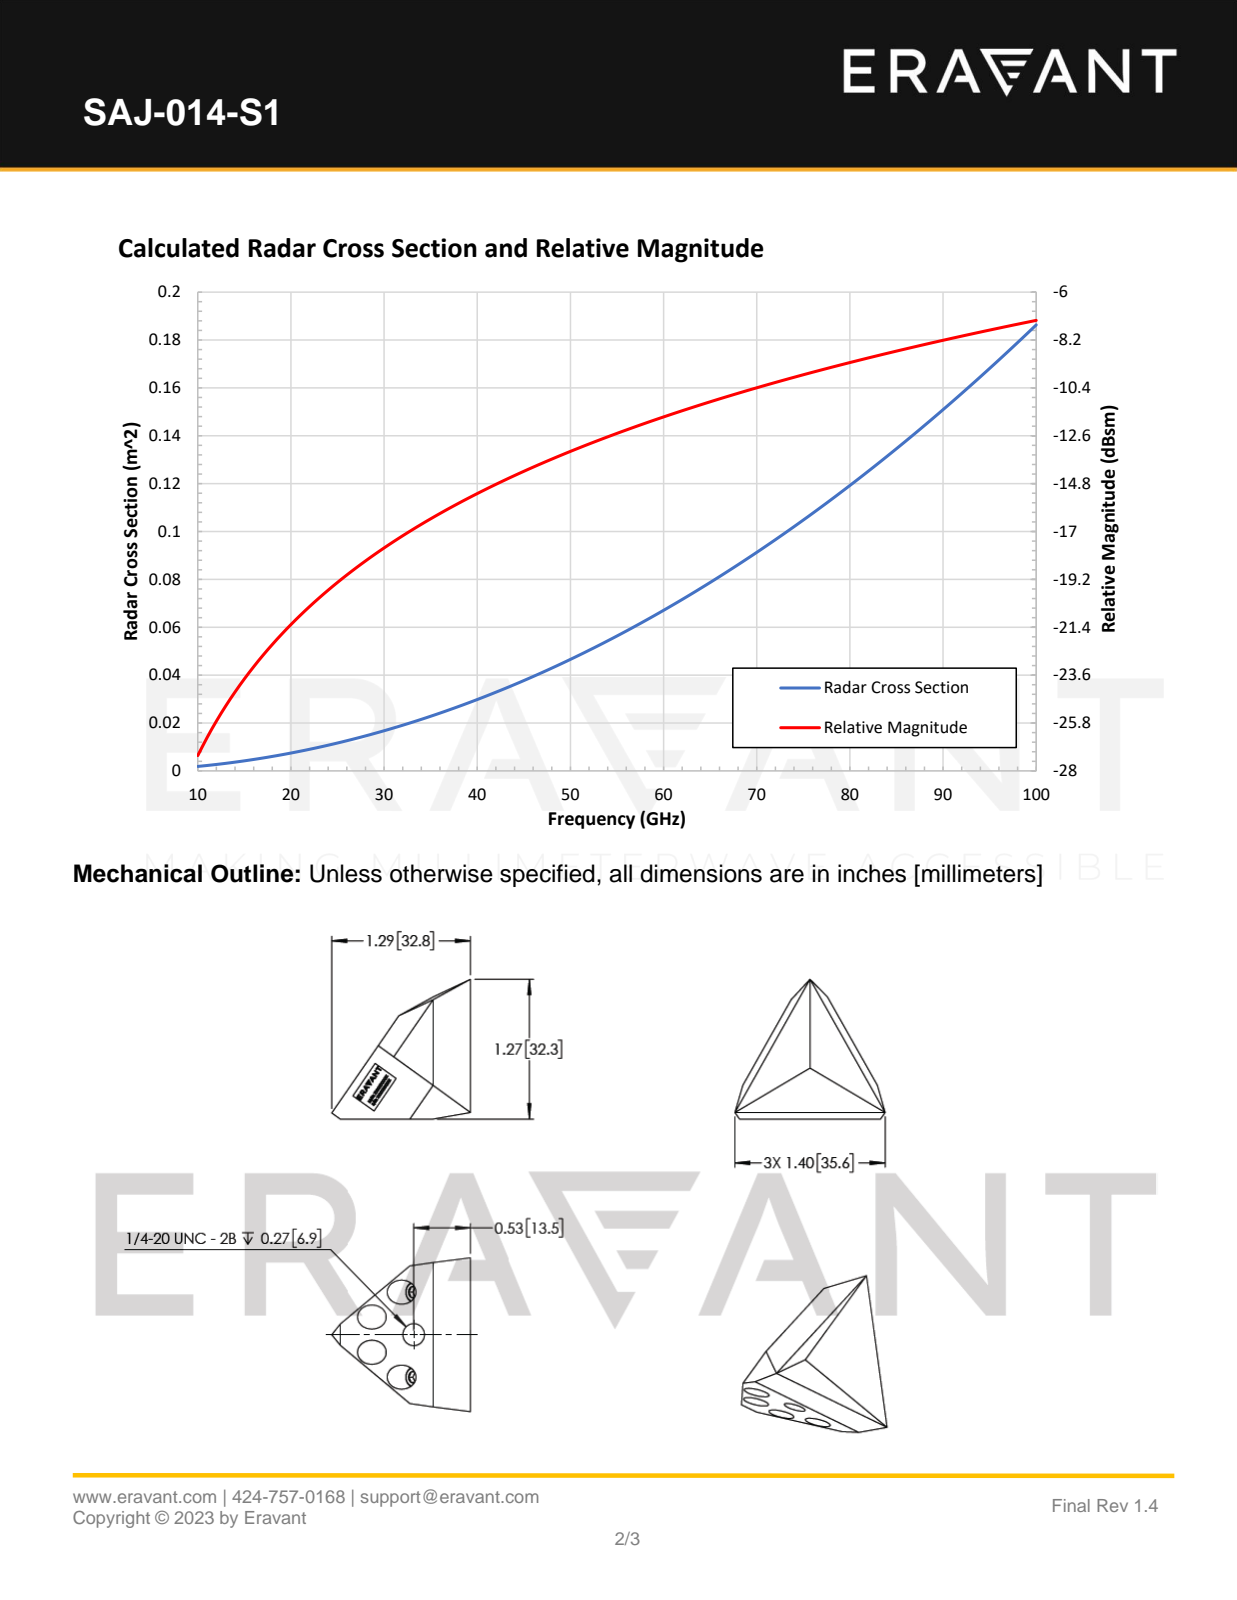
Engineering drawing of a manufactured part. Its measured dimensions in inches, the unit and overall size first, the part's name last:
Units: inches
Overall size (bounding box): 1.74 × 1.4 × 1.054
Round holes (diameter × count): ⌀0.201 ×1
Main face-to-face distances: 0.25, 0.75
Volume: 0.517 in³ · Surface area: 7.068 in²
Bodies: 3 solids, 23 faces (19 planar, 2 cylindrical, 2 other)
Part name (STEP PRODUCT): SAJ-014-S1
STEP written by: SolidWorks 2016 (CONFIG_CONTROL_DESIGN)
